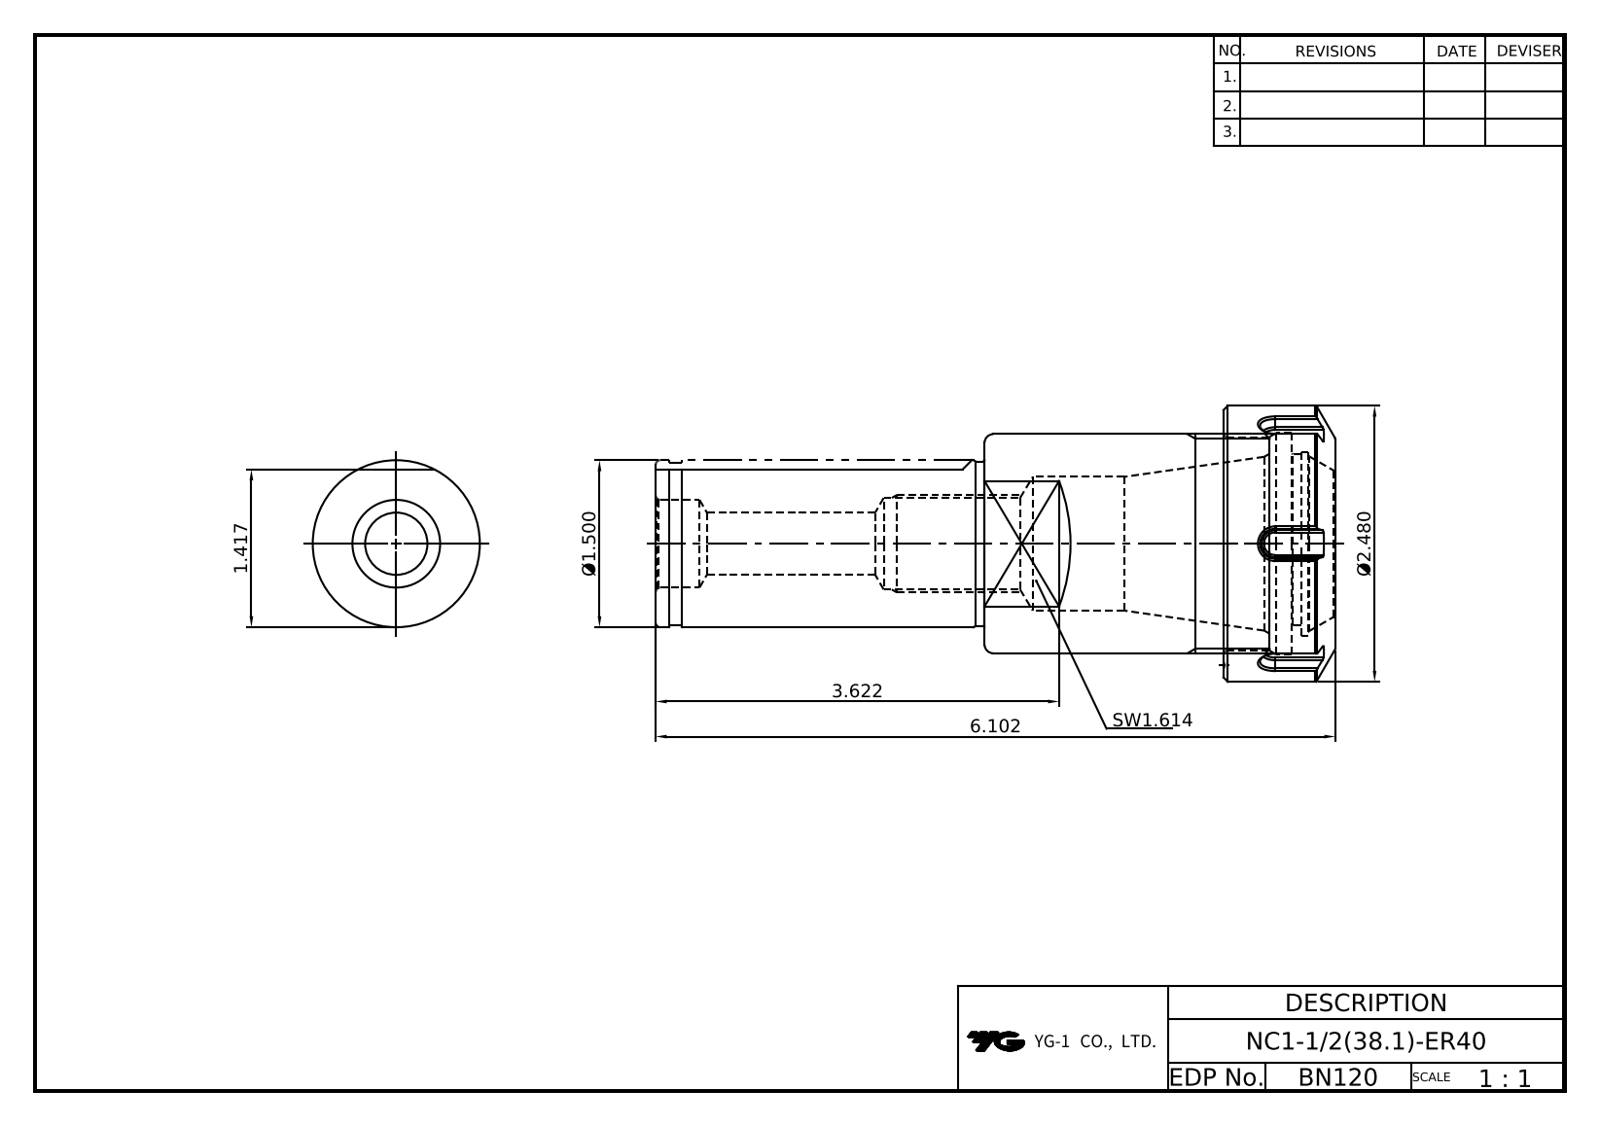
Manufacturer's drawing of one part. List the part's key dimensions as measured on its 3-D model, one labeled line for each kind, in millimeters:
Part name (STEP PRODUCT): LO-NC38.1-ER40; ER40NUT
STEP written by: Autodesk Inventor 2025 (AUTOMOTIVE_DESIGN)
Units: millimetres
Bodies: 2 solids, 111 faces (48 planar, 27 cylindrical, 36 other)
Overall size (bounding box): 155 × 63 × 63
Volume: 177 334 mm³ · Surface area: 44 791 mm²
Round holes (diameter × count): ⌀1.43 ×1, ⌀14.2 ×1, ⌀19.18 ×1, ⌀20 ×1, ⌀30.5 ×1, ⌀33.5 ×1, ⌀38.9 ×1, ⌀41.9 ×1, ⌀48.6 ×1
Round bosses / shafts (diameter × count): ⌀63 ×1, ⌀50 ×1, ⌀38.1 ×1, ⌀37.5 ×1, ⌀37.1 ×1
Partial cylindrical surfaces — rounded edges, fillets, slot ends (radius × count): R0.5 ×12
Main face-to-face distances: 25.5, 1.5, 10.5, 15, 129.5, 140, 155, 80, 141.5, 12
Hole centre spacings: 27.75
